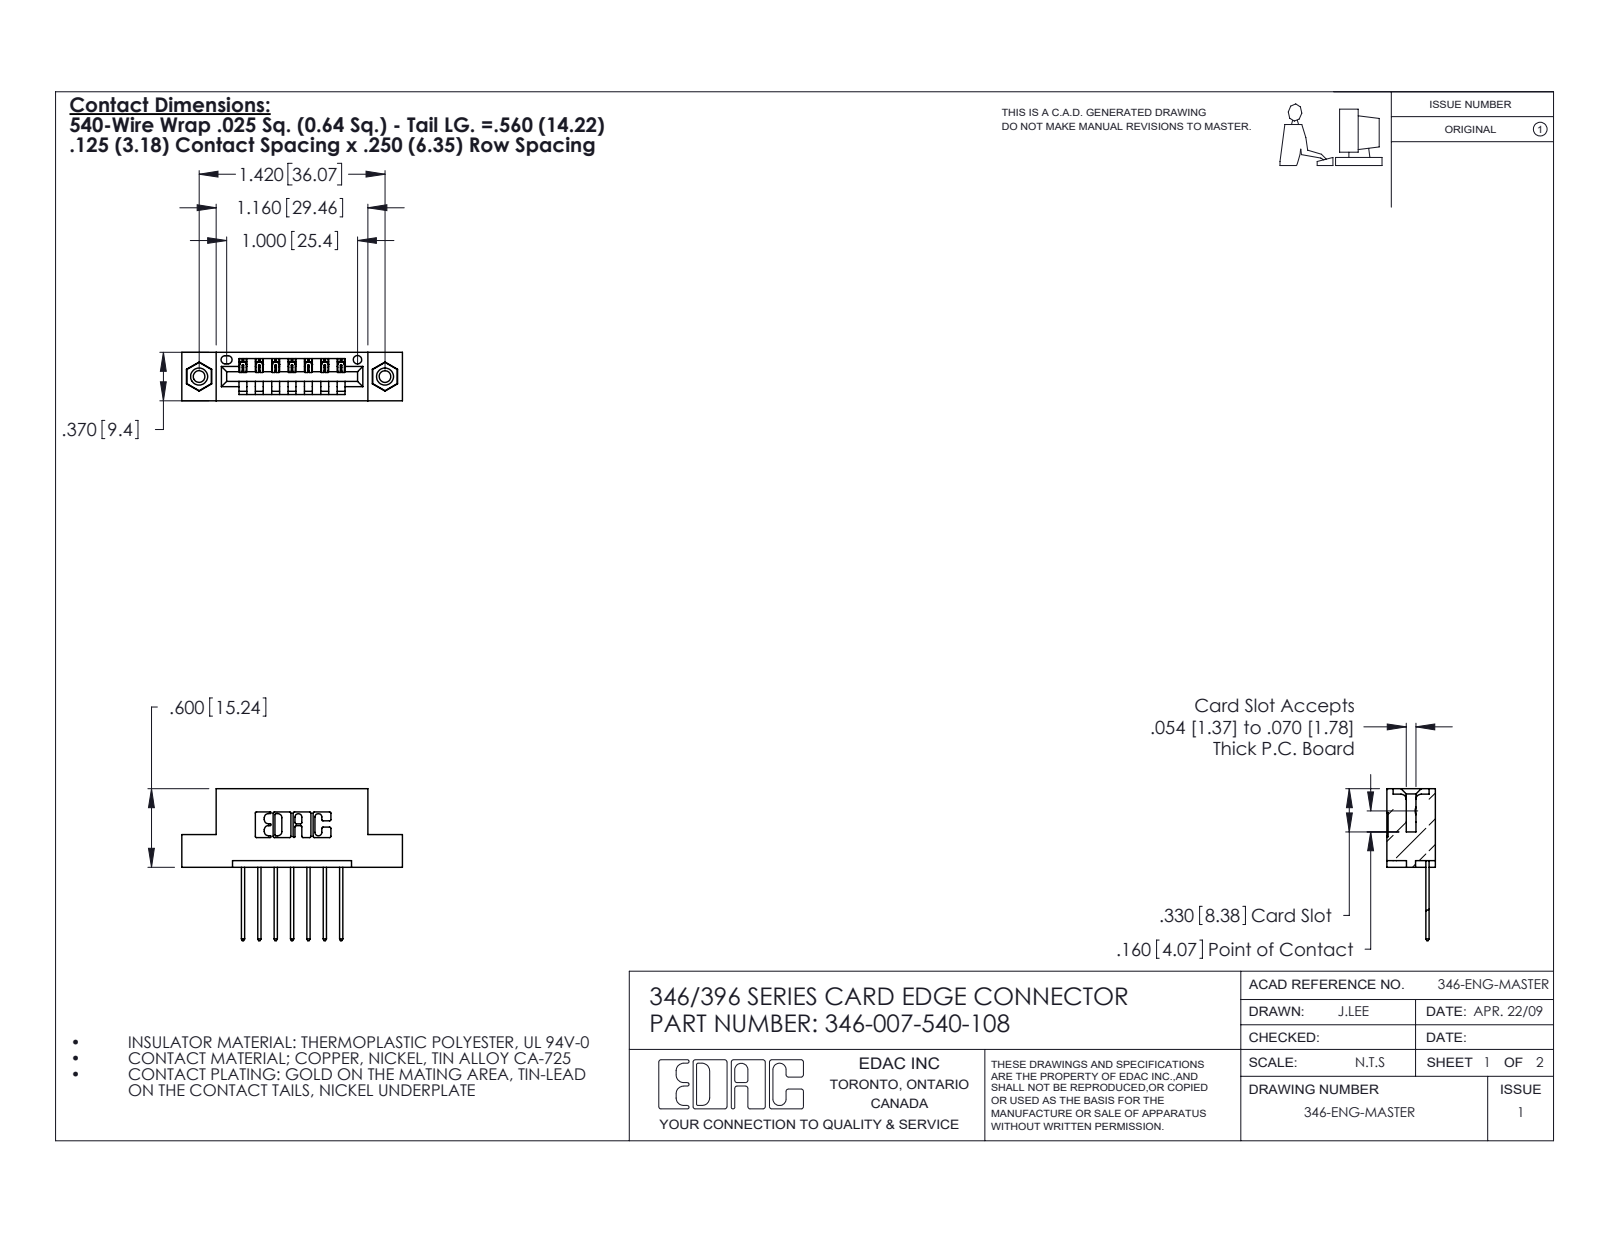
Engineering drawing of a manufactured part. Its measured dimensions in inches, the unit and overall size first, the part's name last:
Units: inches
Overall size (bounding box): 1.685 × 1.16 × 0.37
Round holes (diameter × count): ⌀0.089 ×2, ⌀0.125 ×2, ⌀0.156 ×2, ⌀0.064 ×1
Round bosses / shafts (diameter × count): ⌀0.155 ×2
Partial cylindrical surfaces — rounded edges, fillets, slot ends (radius × count): R0.01 ×22, R0.006 ×14, R0.01 ×14, R0.007 ×6, R0.031 ×6, R0.026 ×3, R0.031 ×2, R0.04 ×2
Main face-to-face distances: 0.25, 0.37, 0.048, 0.322, 0.072, 0.298, 0.025, 0.148, 0.222, 0.1
Hole centre spacings: 0.246, 1.217, 1.42
Volume: 0.235 in³ · Surface area: 7.031 in²
Bodies: 10 solids, 588 faces (388 planar, 184 cylindrical, 16 other)
Part name (STEP PRODUCT): 346 Part_Flush Mounting Lugs - 0.156 Dia-TI; 345-250-001_345-250-003-102; 345-292-001_345-293-140; 346-007-540-108
STEP written by: SolidWorks 2020 (CONFIG_CONTROL_DESIGN)
